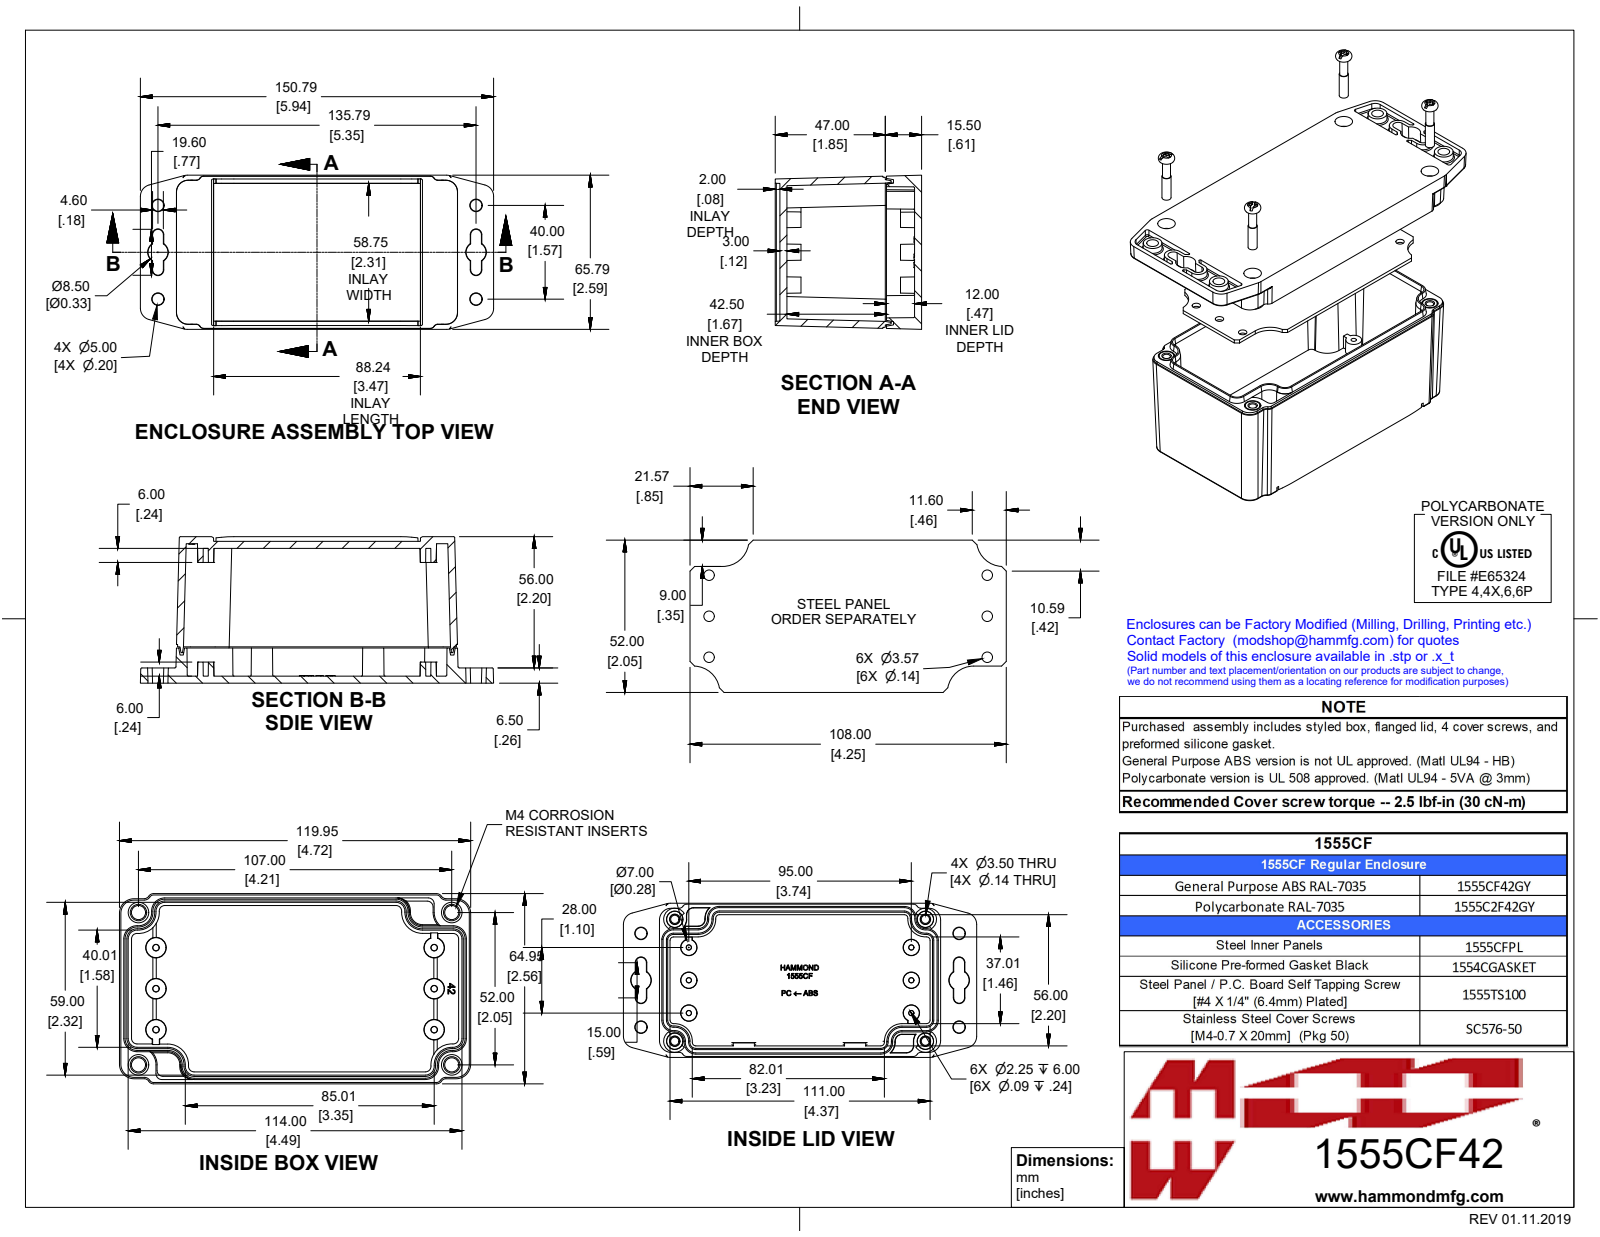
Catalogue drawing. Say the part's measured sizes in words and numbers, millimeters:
The part is named "1555C2F42GY". Its 3-D file was written by "SolidWorks 2019 (CONFIG_CONTROL_DESIGN)". It is 11 solids with 1142 faces: 560 planar, 150 cylindrical and 432 other. Overall it measures 150.8 by 65.8 by 62.5 millimeters. Its volume is 143 000 cubic millimeters and its surface area 101 700 square millimeters. Round holes: 6 of diameter 3, 4 of diameter 3.3, 4 of diameter 3.5, 4 of diameter 7. Round bosses or shafts: 4 of diameter 6.4, 4 of diameter 5.5, 4 of diameter 5.3, 4 of diameter 3.9, 4 of diameter 3.4. Partial cylindrical surfaces (rounded edges, fillets, slot ends): 44 of radius 0.5, 16 of radius 5, 4 of radius 2.3, 4 of radius 4.7, 4 of radius 9, 2 of radius 2, 1 of radius 46.9, 1 of radius 50.4. The main face-to-face distances are 3, 57.5, 9, 6, 48.5, 54.5, 51.5, 60.5, 10.6, 7.6. The hole center spacings are 14, 96, 101.7, 95, 13.4, 13.4, 26.7, 26.7.
